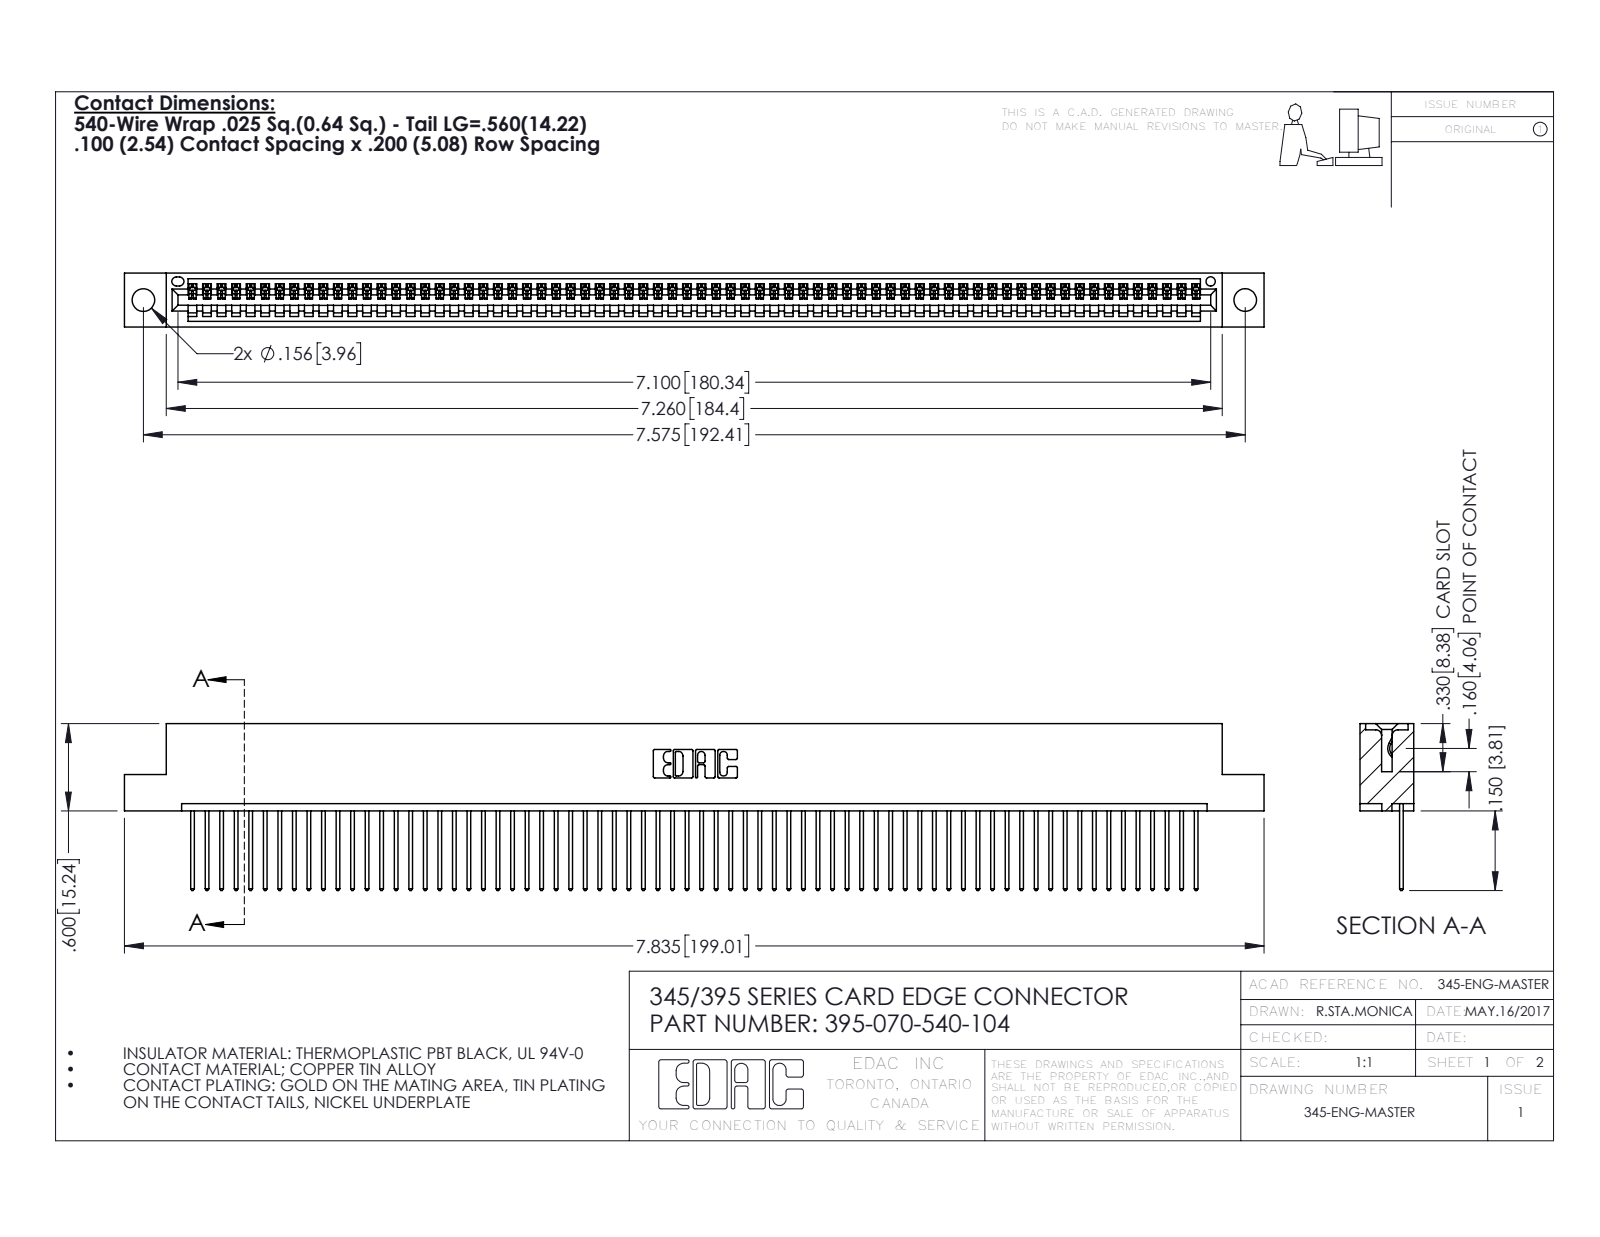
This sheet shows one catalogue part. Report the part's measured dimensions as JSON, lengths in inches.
{"part_name": "395-070-540-104; 345-292-001_345-293-140; 345 Part_Flush Mounting Lugs - 0.156 Dia-TH", "step_written_by": "SolidWorks 2016 (CONFIG_CONTROL_DESIGN)", "units": "inches", "bodies": {"solids": 71, "faces": 4186, "planar": 2880, "cylindrical": 1306, "other": 0}, "overall_size": [7.835, 1.147, 0.37], "volume_in3": 1.168, "surface_area_in2": 40.77, "round_holes": [[0.156, 2], [0.064, 1]], "partial_cylinders_radius": [[0.006, 140], [0.01, 140], [0.01, 22], [0.007, 6], [0.031, 6], [0.026, 3], [0.031, 2], [0.04, 2]], "face_to_face_distances": [0.072, 0.298, 0.37, 0.098, 0.272, 0.025, 0.2, 0.225, 0.149, 0.072], "hole_center_spacings": [0.27, 7.339, 7.575]}
